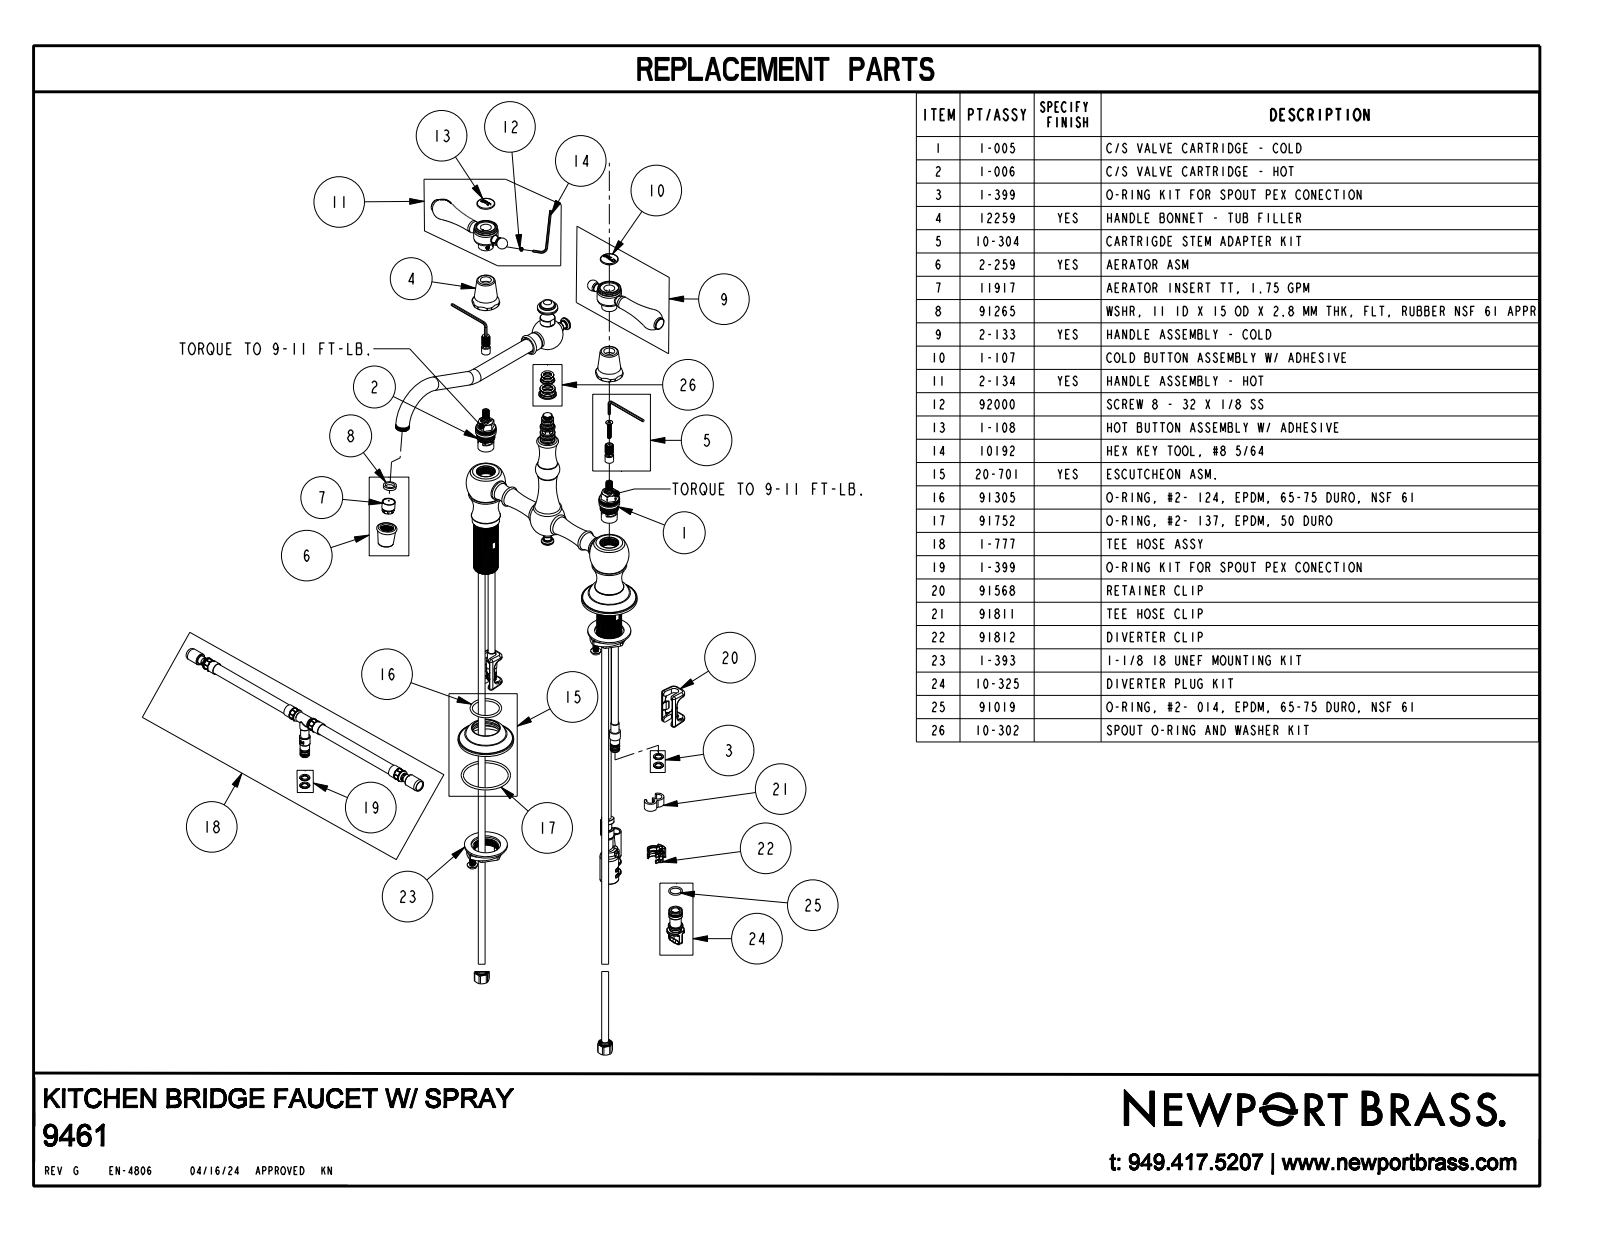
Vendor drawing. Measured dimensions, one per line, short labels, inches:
name: 9461
written by: CREO PARAMETRIC BY PTC INC, 2018400 (AUTOMOTIVE_DESIGN)
unit: in
bodies: 4 solids, 477 faces (123 planar, 112 cylindrical, 242 other)
size: 14.745 × 11.188 × 9.294
volume: 28.19 in³; area: 143.3 in²
holes: 2× ⌀0.855, 1× ⌀0.564, 1× ⌀0.689, 1× ⌀0.812
bosses: 3× ⌀0.625, 2× ⌀2.35, 2× ⌀1.115, 2× ⌀1.055, 2× ⌀0.687, 2× ⌀0.562, 2× ⌀0.405, 2× ⌀0.357
rounds: 7× R0.006, 7× R0.024, 5× R0.03, 3× R0.048, 2× R0.018, 2× R0.036, 2× R0.041, 1× R0.054
face distances: 4.52, 0.02, 4.54, 6.957, 2.437, 2.417, 0.38, 4.14, 4.16, 6.577
hole spacings: 4, 8
